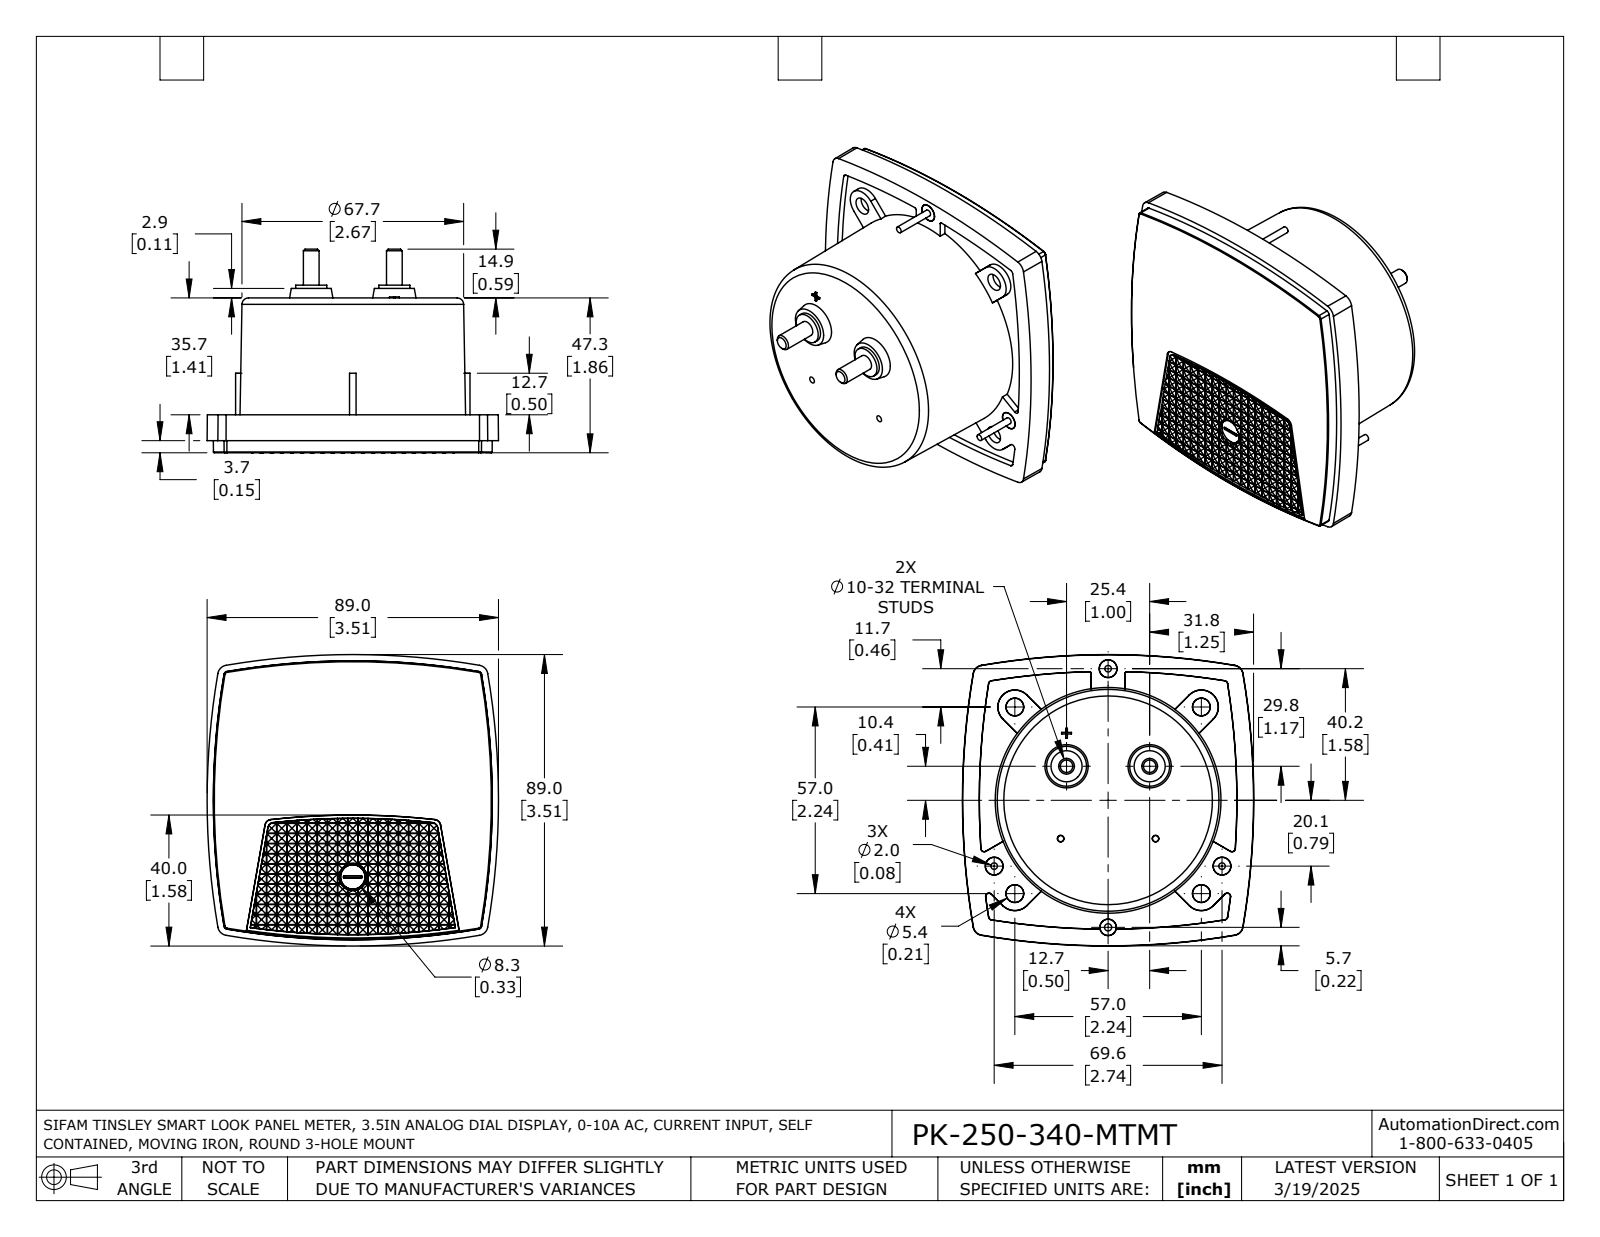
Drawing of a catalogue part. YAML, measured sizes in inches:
part_name: "PK-250-340-MTMT"
step_written_by: "SolidWorks 2021 (AUTOMOTIVE_DESIGN)"
units: inches
bodies: {solids: 1, faces: 1078, planar: 950, cylindrical: 23, other: 105}
overall_size: [3.505, 3.505, 2.453]
volume: 12.99
surface_area: 44.29
round_holes:
  - {diameter: 0.087, count: 1}
round_bosses_or_shafts:
  - {diameter: 0.213, count: 3}
  - {diameter: 0.079, count: 3}
  - {diameter: 0.374, count: 2}
  - {diameter: 0.189, count: 2}
partial_cylinders:
  - {radius: 8.961, count: 1}
face_to_face_distances: [1.862, 1.406, 0.457, 0.079, 1.484, 0.378, 0.024, 0.096, 0.072, 0.12]
